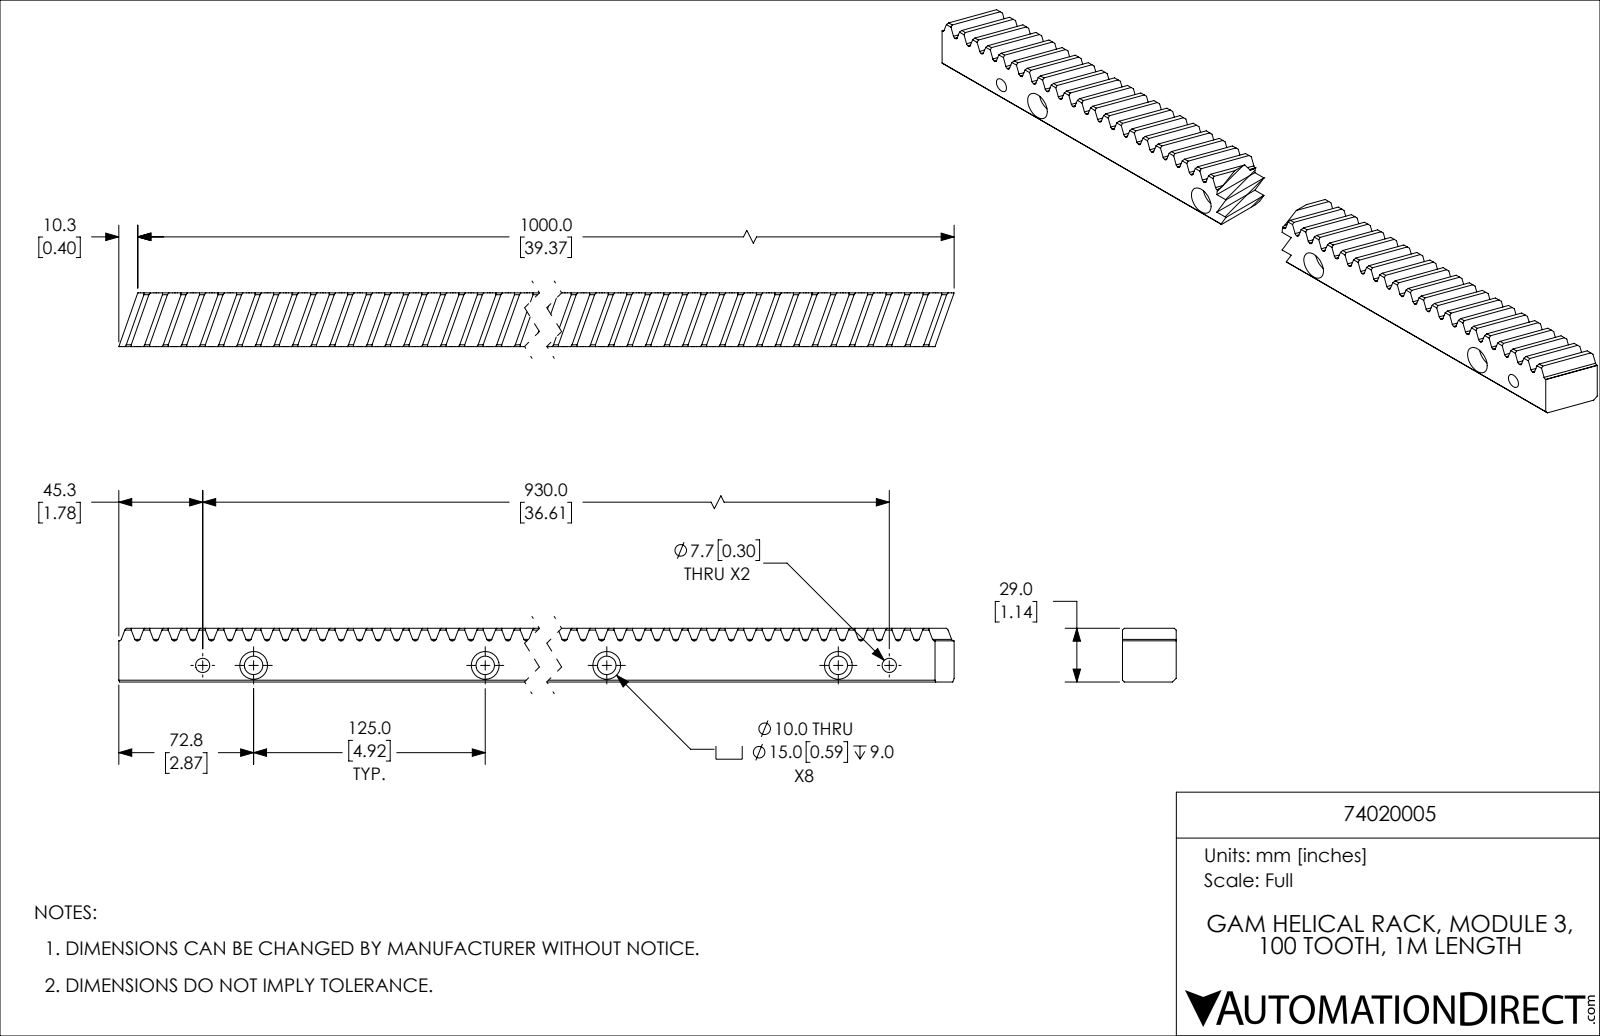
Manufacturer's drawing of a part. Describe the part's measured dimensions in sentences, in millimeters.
The part is named "74020005". Its 3-D file was written by "SolidWorks 2019 (CONFIG_CONTROL_DESIGN)". It is 1 solid with 852 faces: 616 planar, 36 cylindrical and 200 other. Overall it measures 1010.3 by 29 by 29 millimeters. Its volume is 718 700 cubic millimeters and its surface area 145 000 square millimeters. Round holes: 8 of diameter 10, 8 of diameter 15, 2 of diameter 7.7. The main face-to-face distances are 29, 8.9, 26.6, 17.7, 35.4, 70.9, 106.3, 97.5, 124, 88.6. The hole center spacings are 125, 250, 375, 500, 625, 27.5, 152.5, 277.5.
